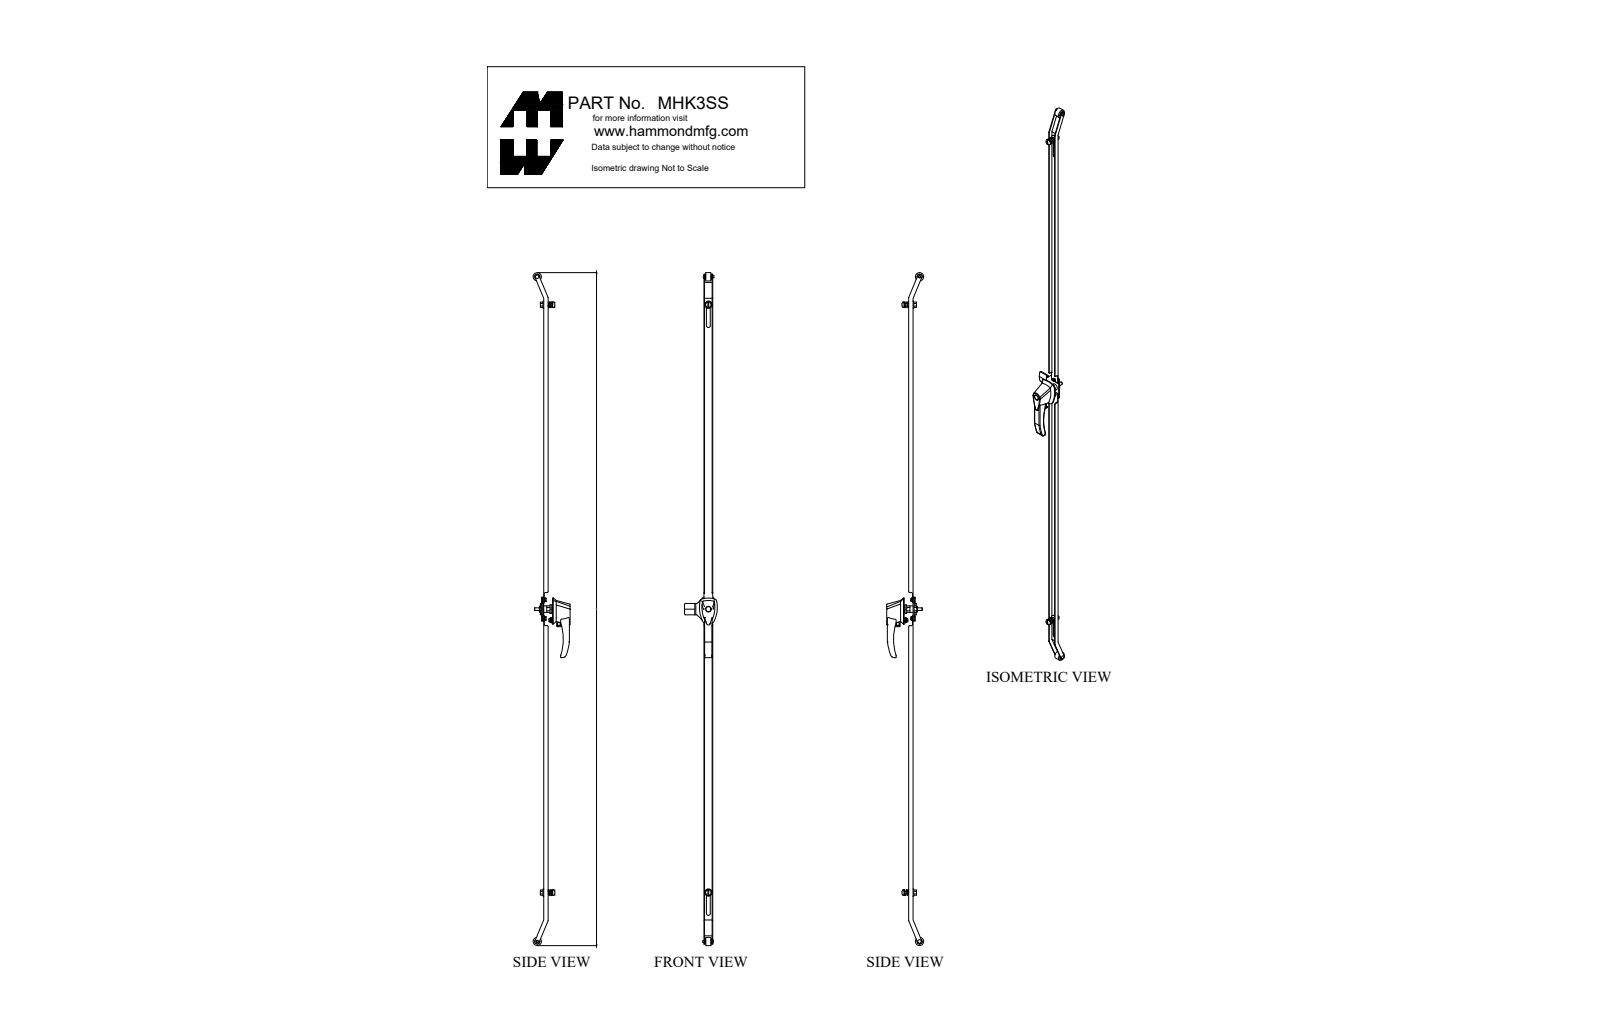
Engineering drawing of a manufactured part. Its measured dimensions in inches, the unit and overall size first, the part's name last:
Units: inches
Overall size (bounding box): 81.493 × 4.473 × 3.975
Round holes (diameter × count): ⌀0.375 ×3, ⌀0.159 ×2, ⌀0.195 ×2, ⌀0.25 ×2, ⌀0.257 ×2, ⌀0.28 ×2, ⌀0.281 ×2, ⌀0.307 ×2, ⌀0.39 ×2, ⌀0.413 ×2, ⌀0.173 ×1, ⌀0.233 ×1
Round bosses / shafts (diameter × count): ⌀1 ×2, ⌀0.882 ×2, ⌀0.678 ×2, ⌀0.63 ×2, ⌀0.402 ×2, ⌀0.375 ×2, ⌀0.325 ×2, ⌀0.278 ×2
Partial cylindrical surfaces — rounded edges, fillets, slot ends (radius × count): R0.125 ×22, R0.03 ×6, R0.06 ×6, R0.09 ×6, R0.01 ×4, R0.234 ×4, R0.312 ×2, R0.75 ×2
Main face-to-face distances: 0.07, 0.992, 1.062, 0.922, 0.531, 0.461, 0.076, 0.986, 0.916, 0.125
Hole centre spacings: 1.126, 1.287, 0.213, 0.625, 1.338, 1.477, 2.251, 2.464
Volume: 24.43 in³ · Surface area: 417.6 in²
Bodies: 34 solids, 555 faces (272 planar, 220 cylindrical, 63 other)
Part name (STEP PRODUCT): MHK3SS
STEP written by: SolidWorks 2018 (AUTOMOTIVE_DESIGN)
